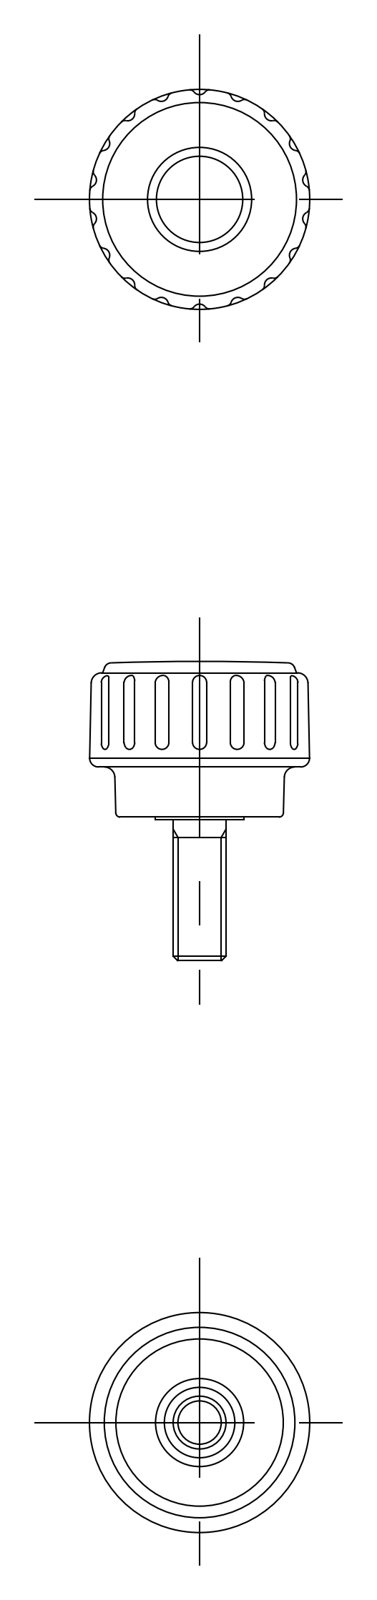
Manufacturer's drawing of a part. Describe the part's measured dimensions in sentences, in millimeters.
The part is named "screw; knob; KDM_25_M6_16_23236_36". Its 3-D file was written by "CADfix (AUTOMOTIVE_DESIGN)". It is 2 solids with 110 faces: 0 planar, 0 cylindrical and 110 other. Overall it measures 33.94 by 24.96 by 24.96 millimeters. Its volume is 7 531 cubic millimeters and its surface area 3 035 square millimeters.
